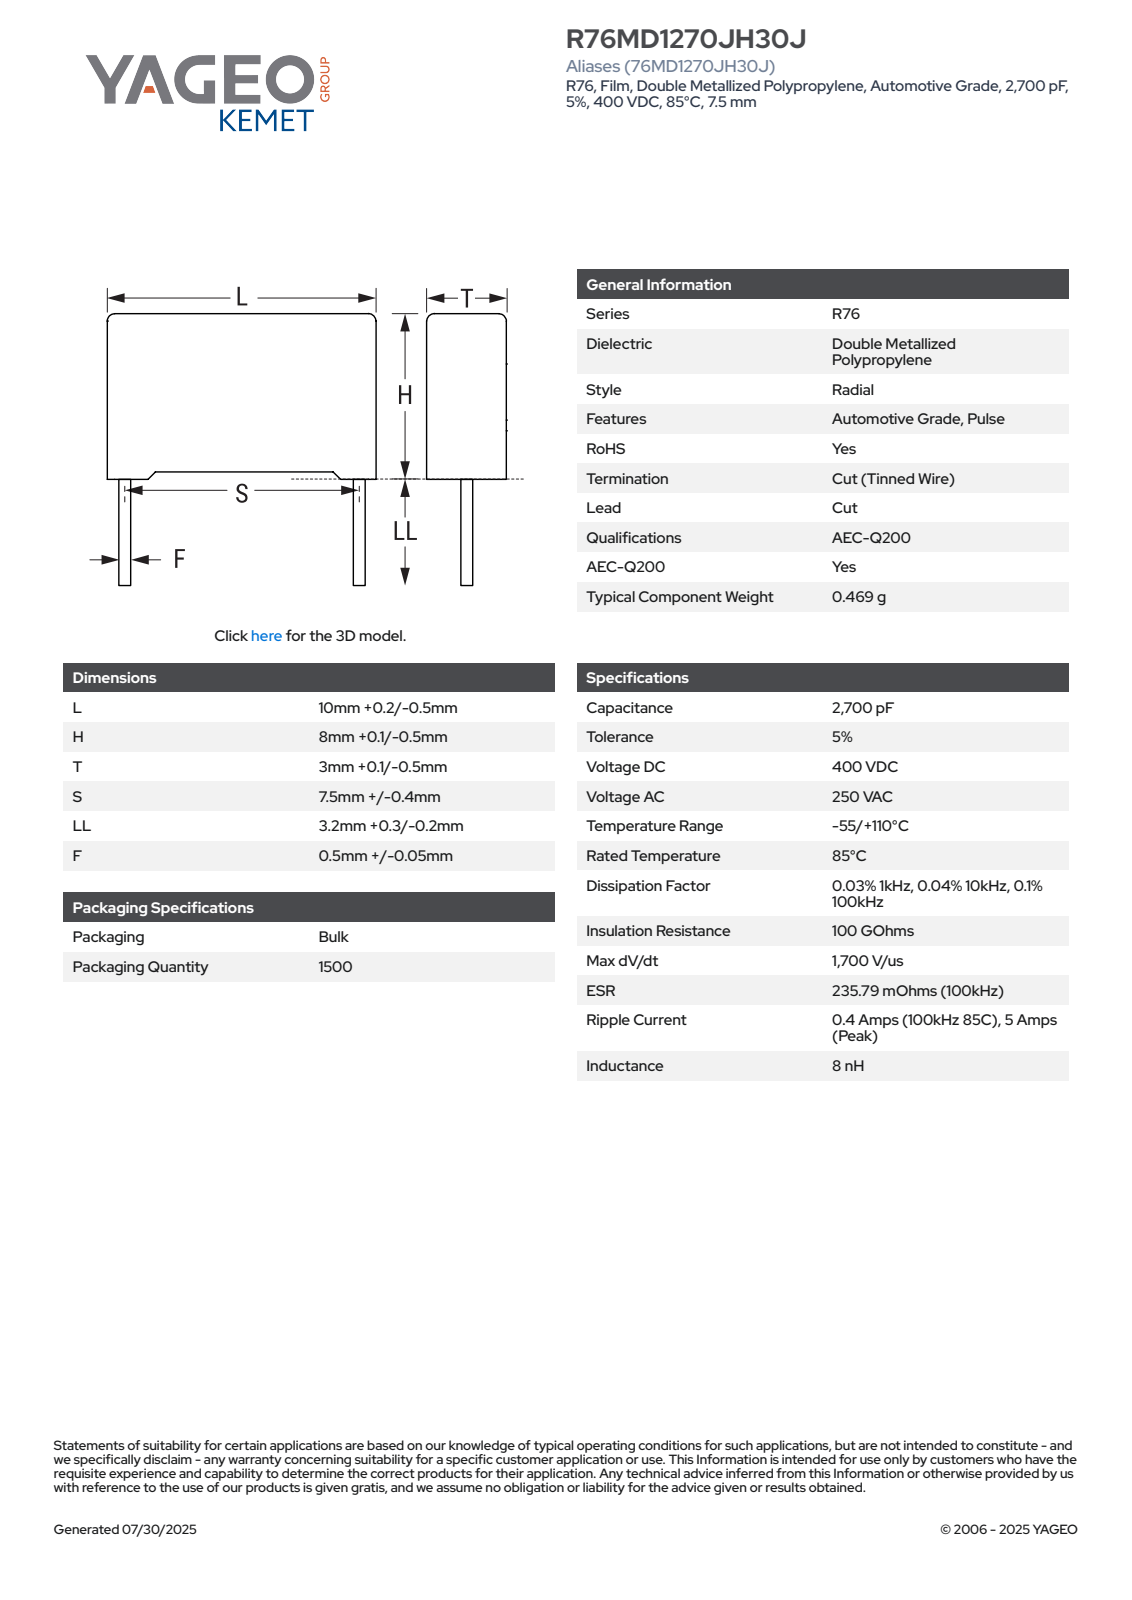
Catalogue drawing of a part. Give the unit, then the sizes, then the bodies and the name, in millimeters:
Units: millimetres
Overall size (bounding box): 11.6 × 10.2 × 3.1
Round bosses / shafts (diameter × count): ⌀0.55 ×2
Partial cylindrical surfaces — rounded edges, fillets, slot ends (radius × count): R0.5 ×4
Main face-to-face distances: 3.1, 10.2, 7.35, 0.34, 2.76, 2.42, 0.75, 8.1, 9.86, 0.47
Volume: 239 mm³ · Surface area: 309 mm²
Bodies: 4 solids, 85 faces (77 planar, 8 cylindrical, 0 other)
Part name (STEP PRODUCT): CFR_RB2_10X8X3_L10.2H8.1T3.1S7.5LL3.5F0.55
STEP written by: SolidWorks 2021 (AUTOMOTIVE_DESIGN)
